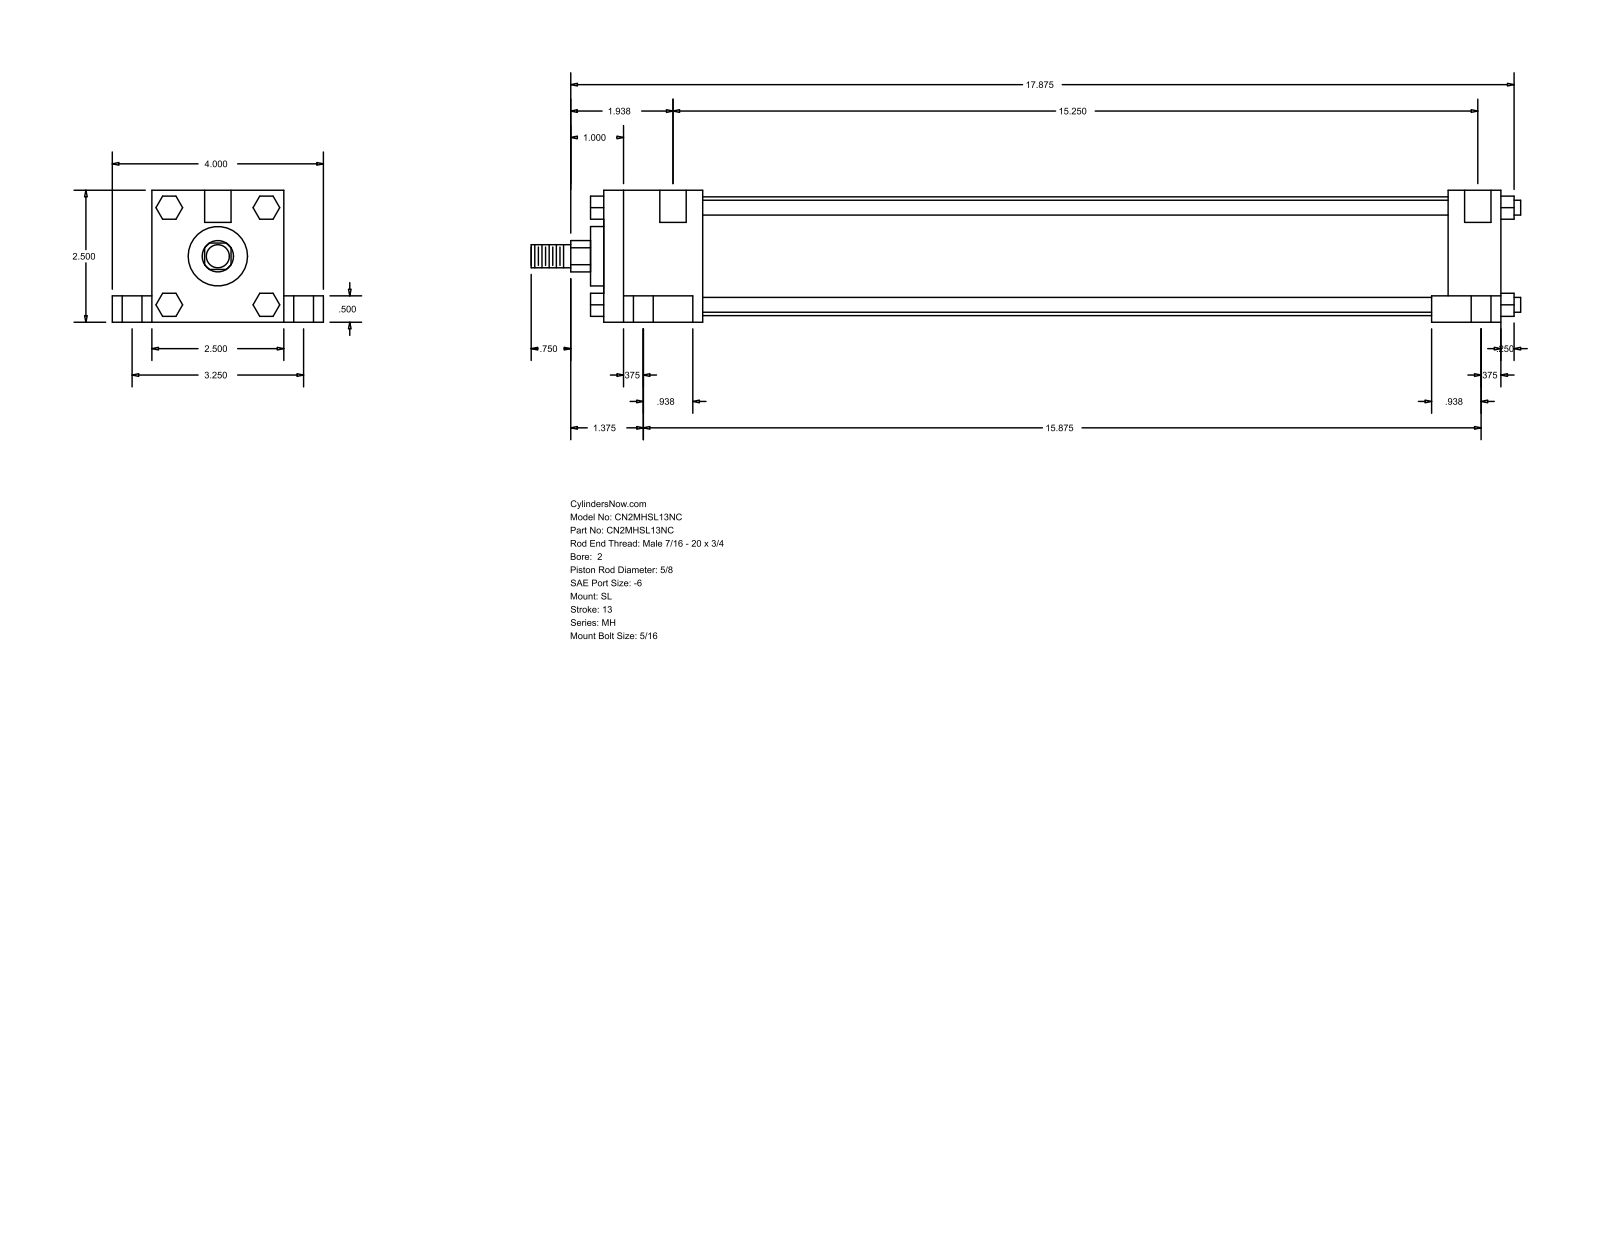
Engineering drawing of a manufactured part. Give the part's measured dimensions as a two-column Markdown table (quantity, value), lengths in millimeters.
| quantity | value |
| --- | --- |
| part name | MH_SL__0200_0.625 |
| STEP written by | GSSL Pune (CONFIG_CONTROL_DESIGN) |
| units | millimeters |
| bodies | 0 solids, 148 faces (112 planar, 36 cylindrical, 0 other) |
| overall size | 476.25 × 101.6 × 63.5 |
| round holes (diameter × count) | 5.56 × 4, 9.53 × 4, 15.88 × 4, 12.7 × 2 |
| round bosses / shafts (diameter × count) | 7.14 × 4, 57.15 × 1, 28.57 × 1, 15.88 × 1, 11.11 × 1 |
| partial cylindrical surfaces (radius × count) | 7.54 × 1 |
| main face-to-face distances | 63.5, 431.8, 12.7, 19.05, 82.55, 50.8, 406.39, 25.41, 47.62, 358.77 |
| hole center spacings | 41.3, 42.36, 43.67, 82.54, 391.12, 395.29, 395.86, 403.23 |
